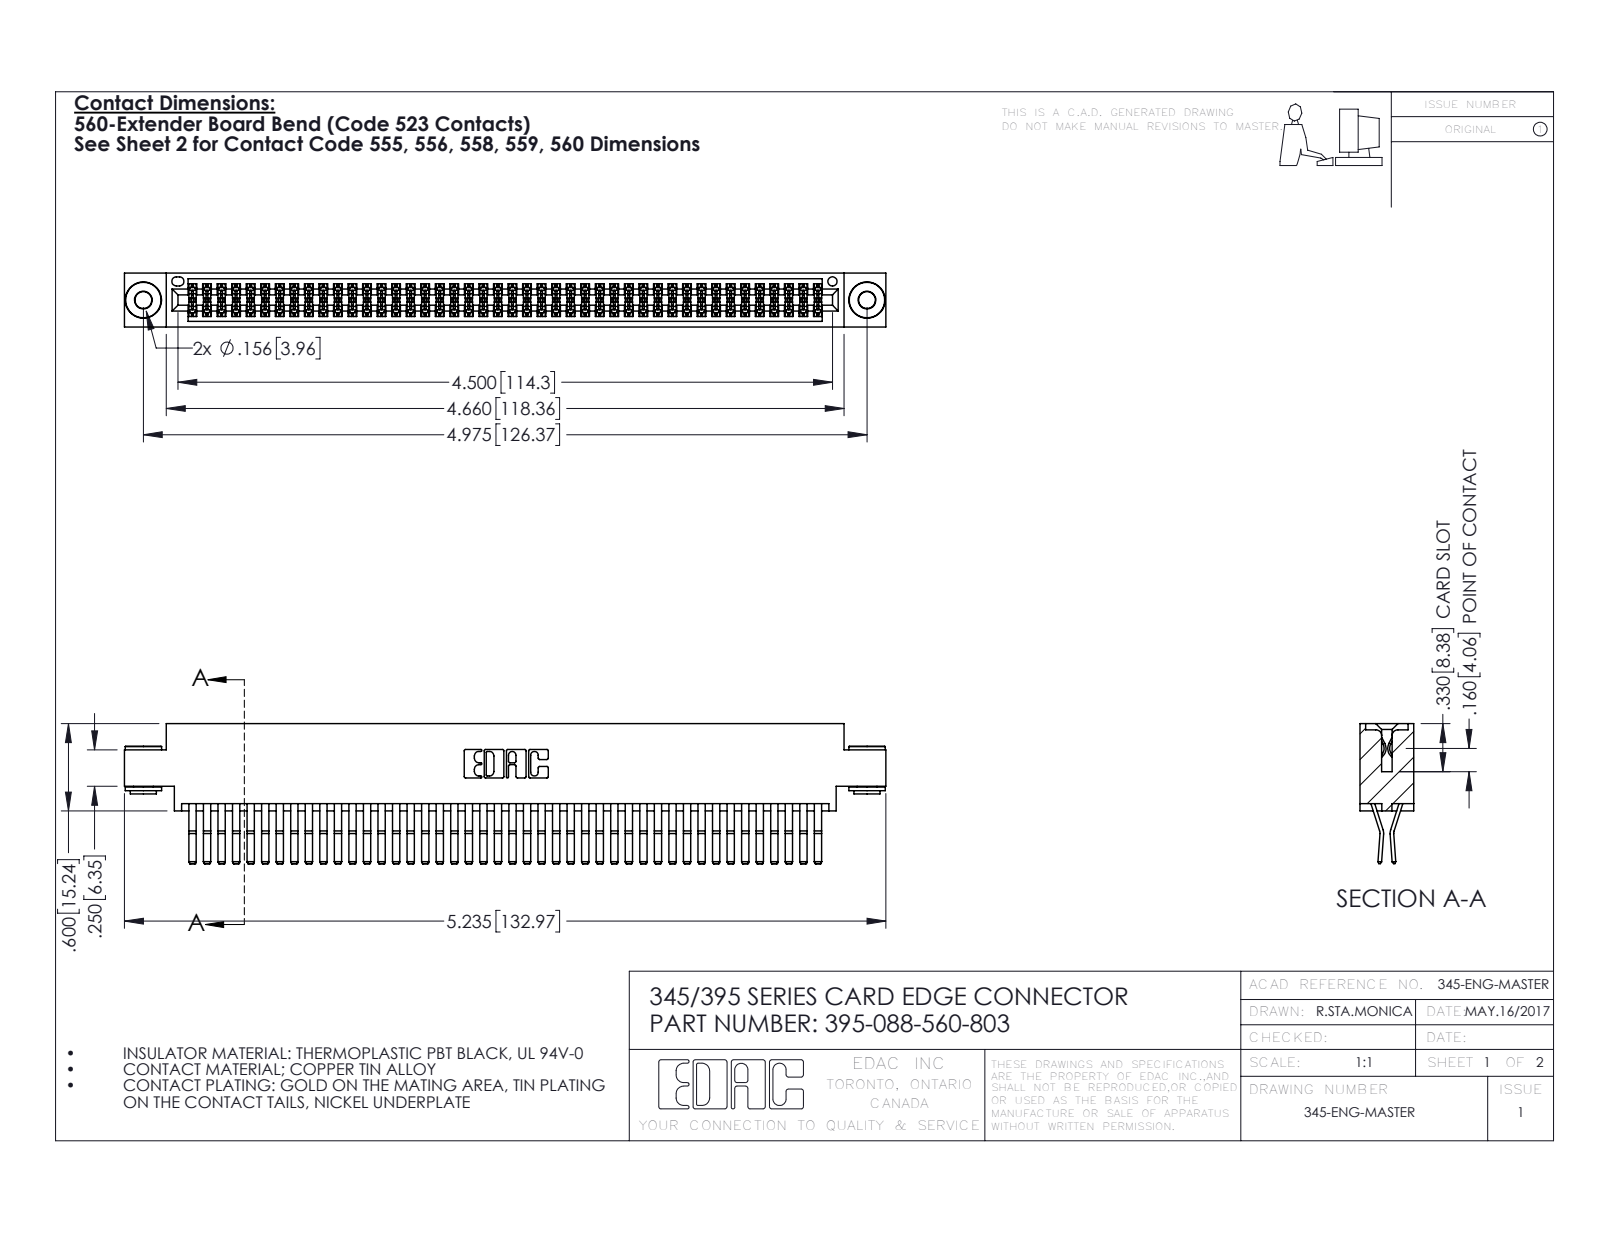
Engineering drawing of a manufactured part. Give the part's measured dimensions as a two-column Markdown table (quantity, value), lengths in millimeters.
| quantity | value |
| --- | --- |
| part name | 395-088-560-803; 345-250-002_345-250-002-102; 345-292-001_560 Tail; 345 Part_0.170 Offset - 0.156 Dia-TH |
| STEP written by | SolidWorks 2016 (CONFIG_CONTROL_DESIGN) |
| units | millimeters |
| bodies | 91 solids, 4744 faces (2998 planar, 1738 cylindrical, 8 other) |
| overall size | 133 × 24.4 × 9.4 |
| volume | 13 400 mm³ |
| surface area | 21 700 mm² |
| round holes (diameter × count) | 2.9 × 2, 4 × 2, 1.6 × 1 |
| round bosses / shafts (diameter × count) | 6.4 × 2, 4.6 × 2, 3.5 × 2 |
| partial cylindrical surfaces (radius × count) | 0.2 × 132, 0.3 × 22, 0.2 × 6, 0.8 × 6, 0.7 × 3, 0.3 × 2, 0.4 × 2, 0.5 × 2 |
| main face-to-face distances | 0.6, 1.8, 7.6, 9.4, 5.1, 2.5, 6.9, 5.7, 4.4, 3.8 |
| hole center spacings | 6.9, 120.4, 126.4 |
